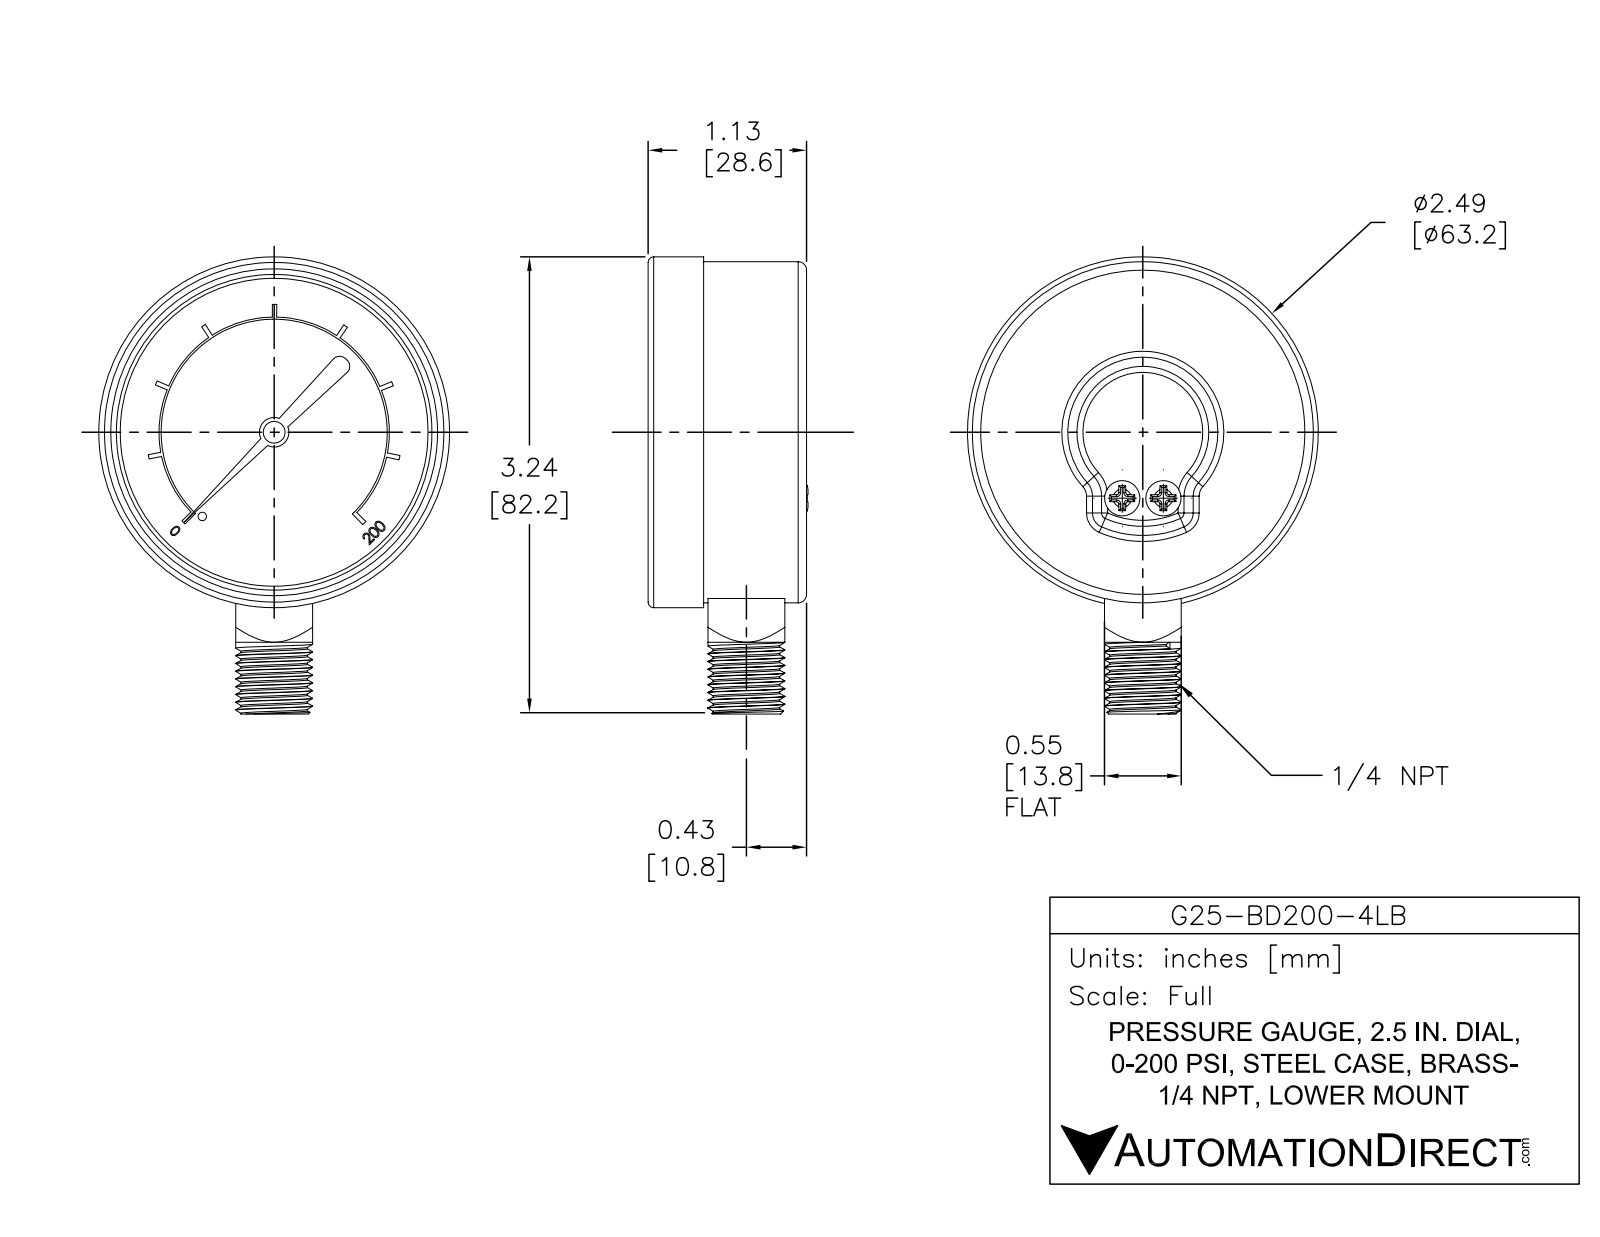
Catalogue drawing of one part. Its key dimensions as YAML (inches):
part_name: "G25-BD200-4LB"
step_written_by: "SolidWorks 2021 (AUTOMOTIVE_DESIGN)"
units: inches
bodies: {solids: 1, faces: 220, planar: 115, cylindrical: 35, other: 70}
overall_size: [3.245, 2.49, 1.135]
volume: 4.288
surface_area: 22.39
round_holes:
  - {diameter: 0.14, count: 1}
  - {diameter: 2.185, count: 1}
round_bosses_or_shafts:
  - {diameter: 0.25, count: 2}
  - {diameter: 2.49, count: 1}
  - {diameter: 2.421, count: 1}
  - {diameter: 0.545, count: 1}
  - {diameter: 0.154, count: 1}
  - {diameter: 0.123, count: 1}
  - {diameter: 0.06, count: 1}
partial_cylinders:
  - {radius: 0.06, count: 6}
  - {radius: 0.105, count: 1}
  - {radius: 0.803, count: 1}
  - {radius: 0.818, count: 1}
face_to_face_distances: [0.835, 0.1, 0.735, 1.125, 1.025, 0.29, 0.545, 0.731, 0.631, 0.104]
